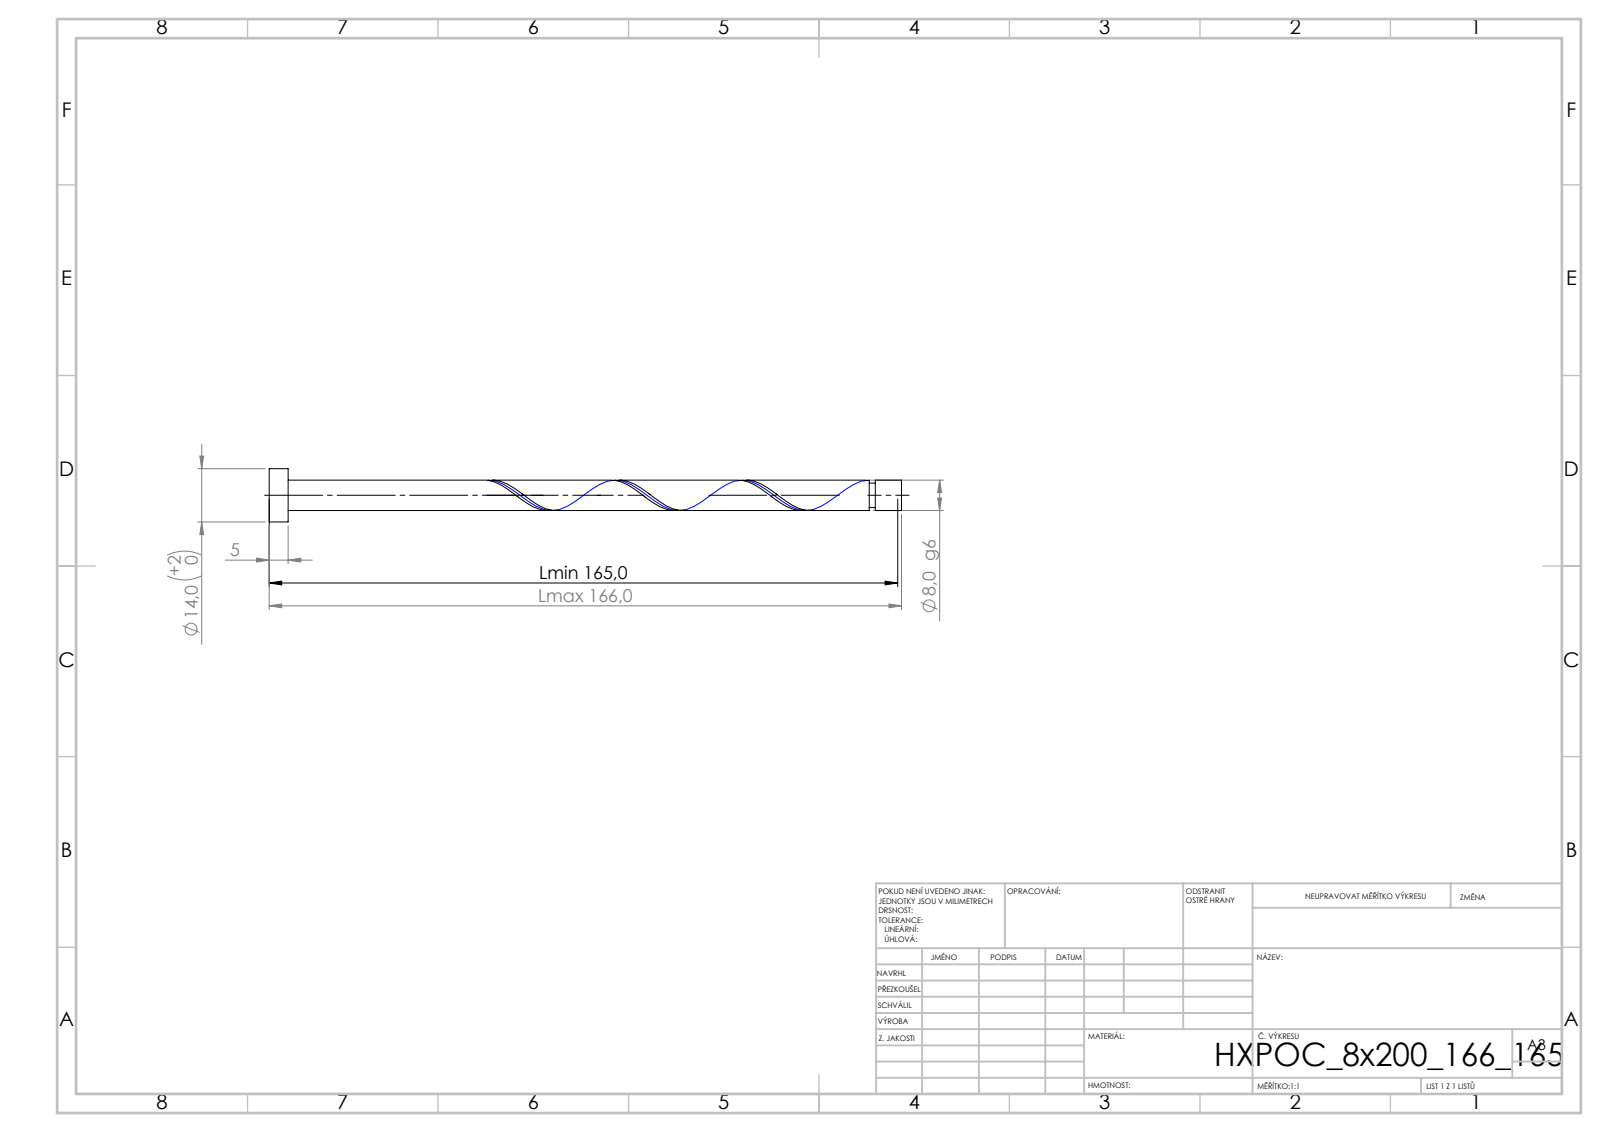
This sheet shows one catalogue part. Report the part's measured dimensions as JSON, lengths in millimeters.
{"step_written_by": "SolidWorks 2019 (CONFIG_CONTROL_DESIGN)", "units": "millimeters", "bodies": {"solids": 1, "faces": 21, "planar": 6, "cylindrical": 14, "other": 1}, "overall_size": [166, 14, 14], "volume_mm3": 8737, "surface_area_mm2": 4706, "round_bosses_or_shafts": [[14, 1], [8, 1], [6.4, 1]], "face_to_face_distances": [5, 166, 161, 159.12, 154.12, 6.88, 157.52, 152.52, 1.6, 8.48]}
